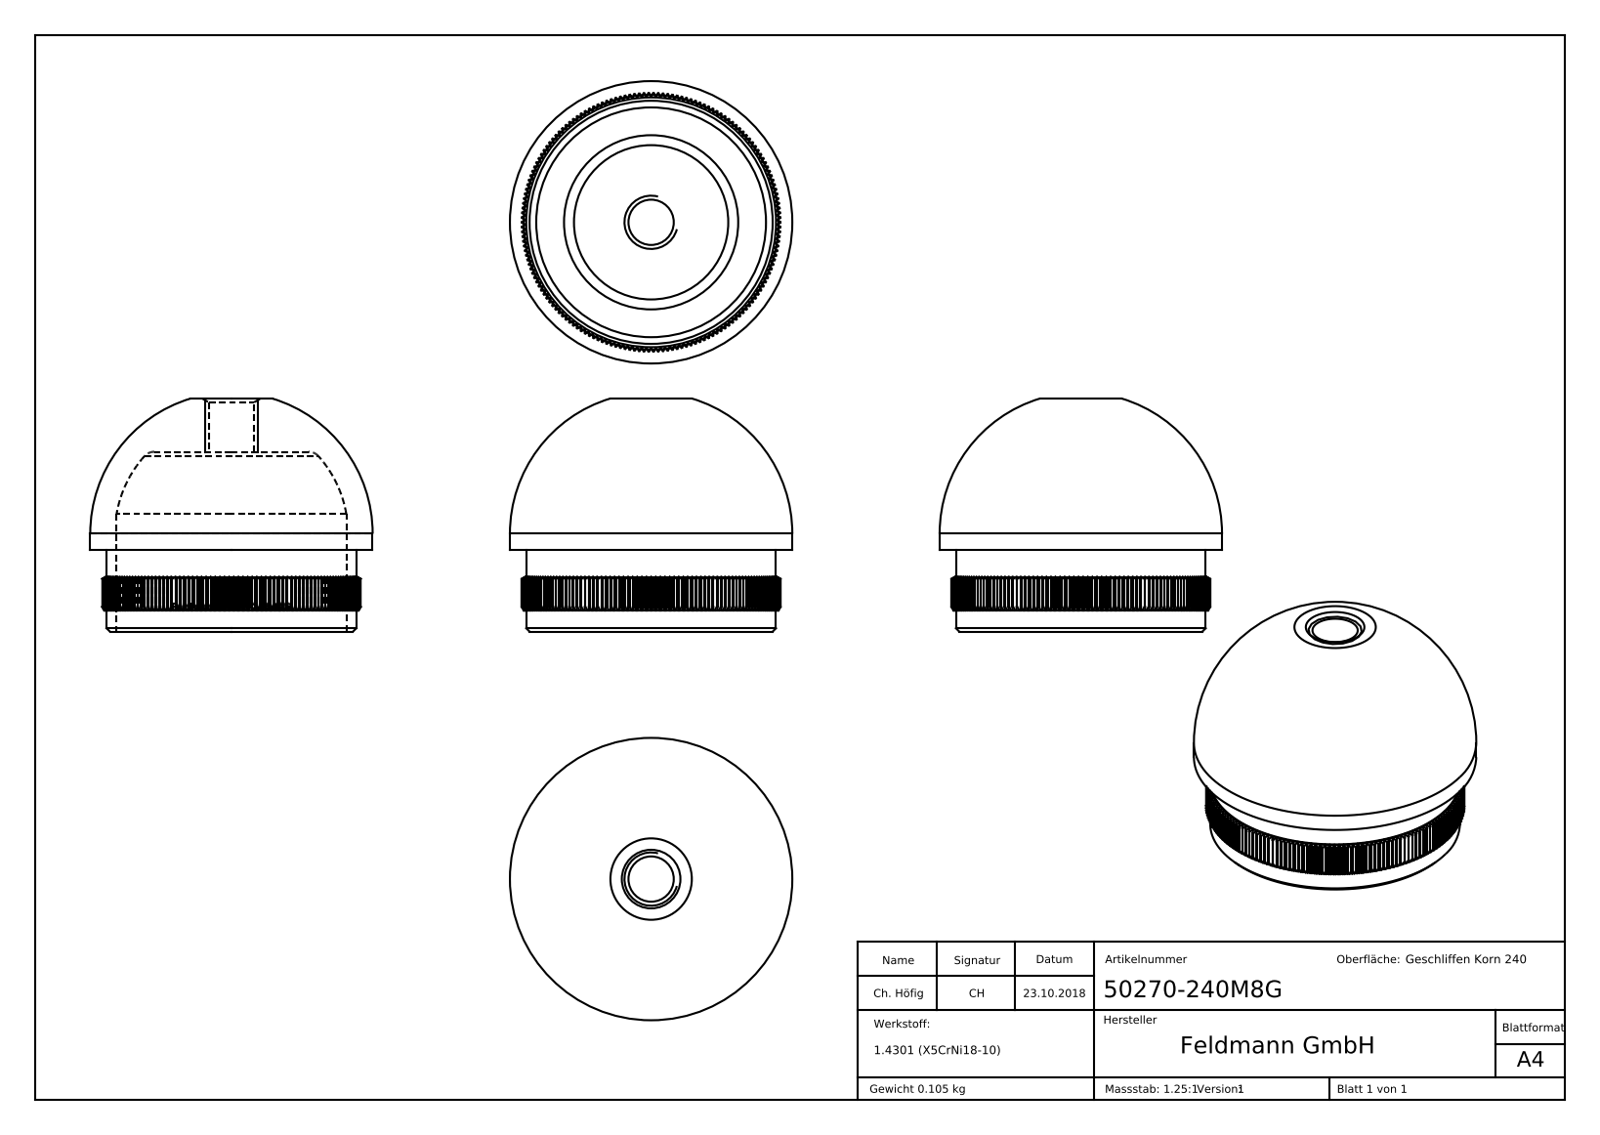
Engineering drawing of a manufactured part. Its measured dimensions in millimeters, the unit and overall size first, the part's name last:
Units: millimetres
Overall size (bounding box): 42.4 × 42.4 × 35
Round holes (diameter × count): ⌀6.8 ×1, ⌀34.5 ×1
Round bosses / shafts (diameter × count): ⌀42.4 ×1, ⌀37.5 ×1
Partial cylindrical surfaces — rounded edges, fillets, slot ends (radius × count): R17.35 ×1, R19.4 ×1
Main face-to-face distances: 14.8, 18.9, 12.2, 27, 18.92, 18.88, 8, 35, 22.8, 3.2
Volume: 13 284 mm³ · Surface area: 9 110 mm²
Bodies: 1 solid, 1105 faces (451 planar, 207 cylindrical, 447 other)
Part name (STEP PRODUCT): 50270-240M8G
STEP written by: SolidWorks 2015 (CONFIG_CONTROL_DESIGN)
